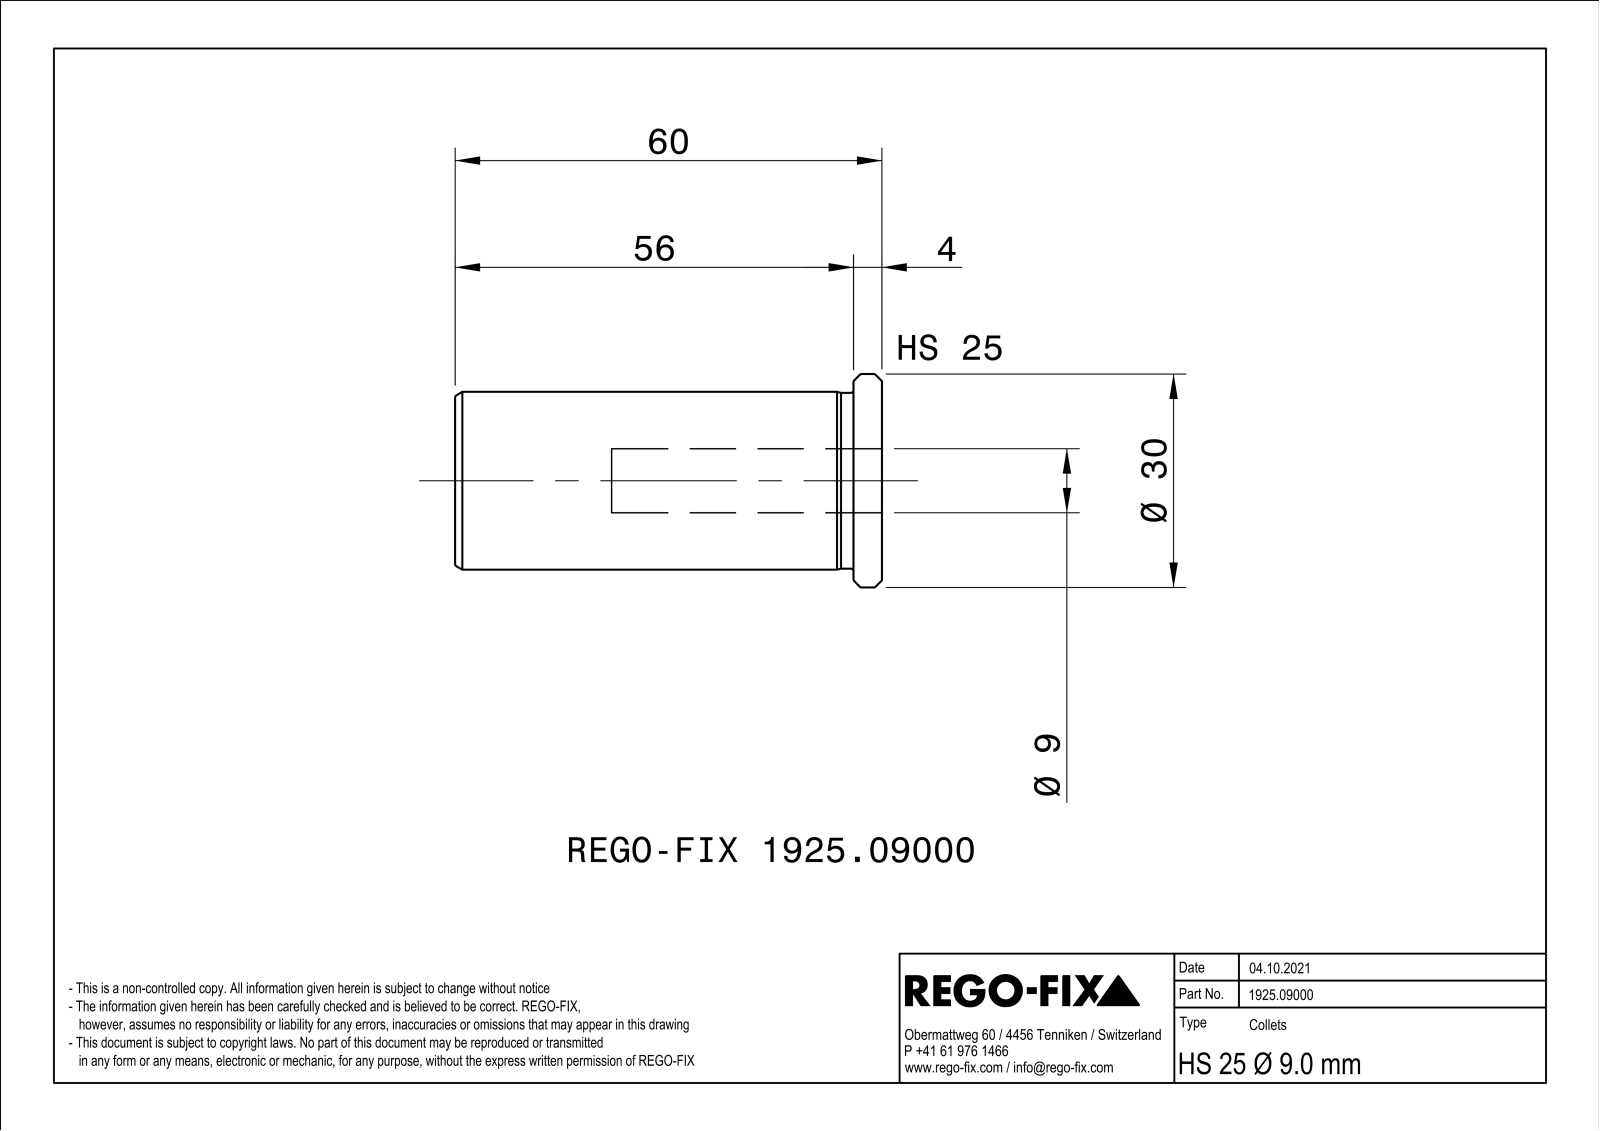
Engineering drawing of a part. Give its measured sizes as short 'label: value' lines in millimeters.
name: NOCUT
written by: SIEMENS PLM Software Solid Edge ST10 (AUTOMOTIVE_DESIGN)
unit: mm
bodies: 1 solid, 73 faces (22 planar, 12 cylindrical, 39 other)
size: 60 × 29.99 × 29.99
volume: 22 093 mm³; area: 9 843 mm²
holes: 1× ⌀9, 1× ⌀10, 1× ⌀20.5
bosses: 1× ⌀30, 1× ⌀25, 1× ⌀24.7
face distances: 0.8, 4, 60, 56
